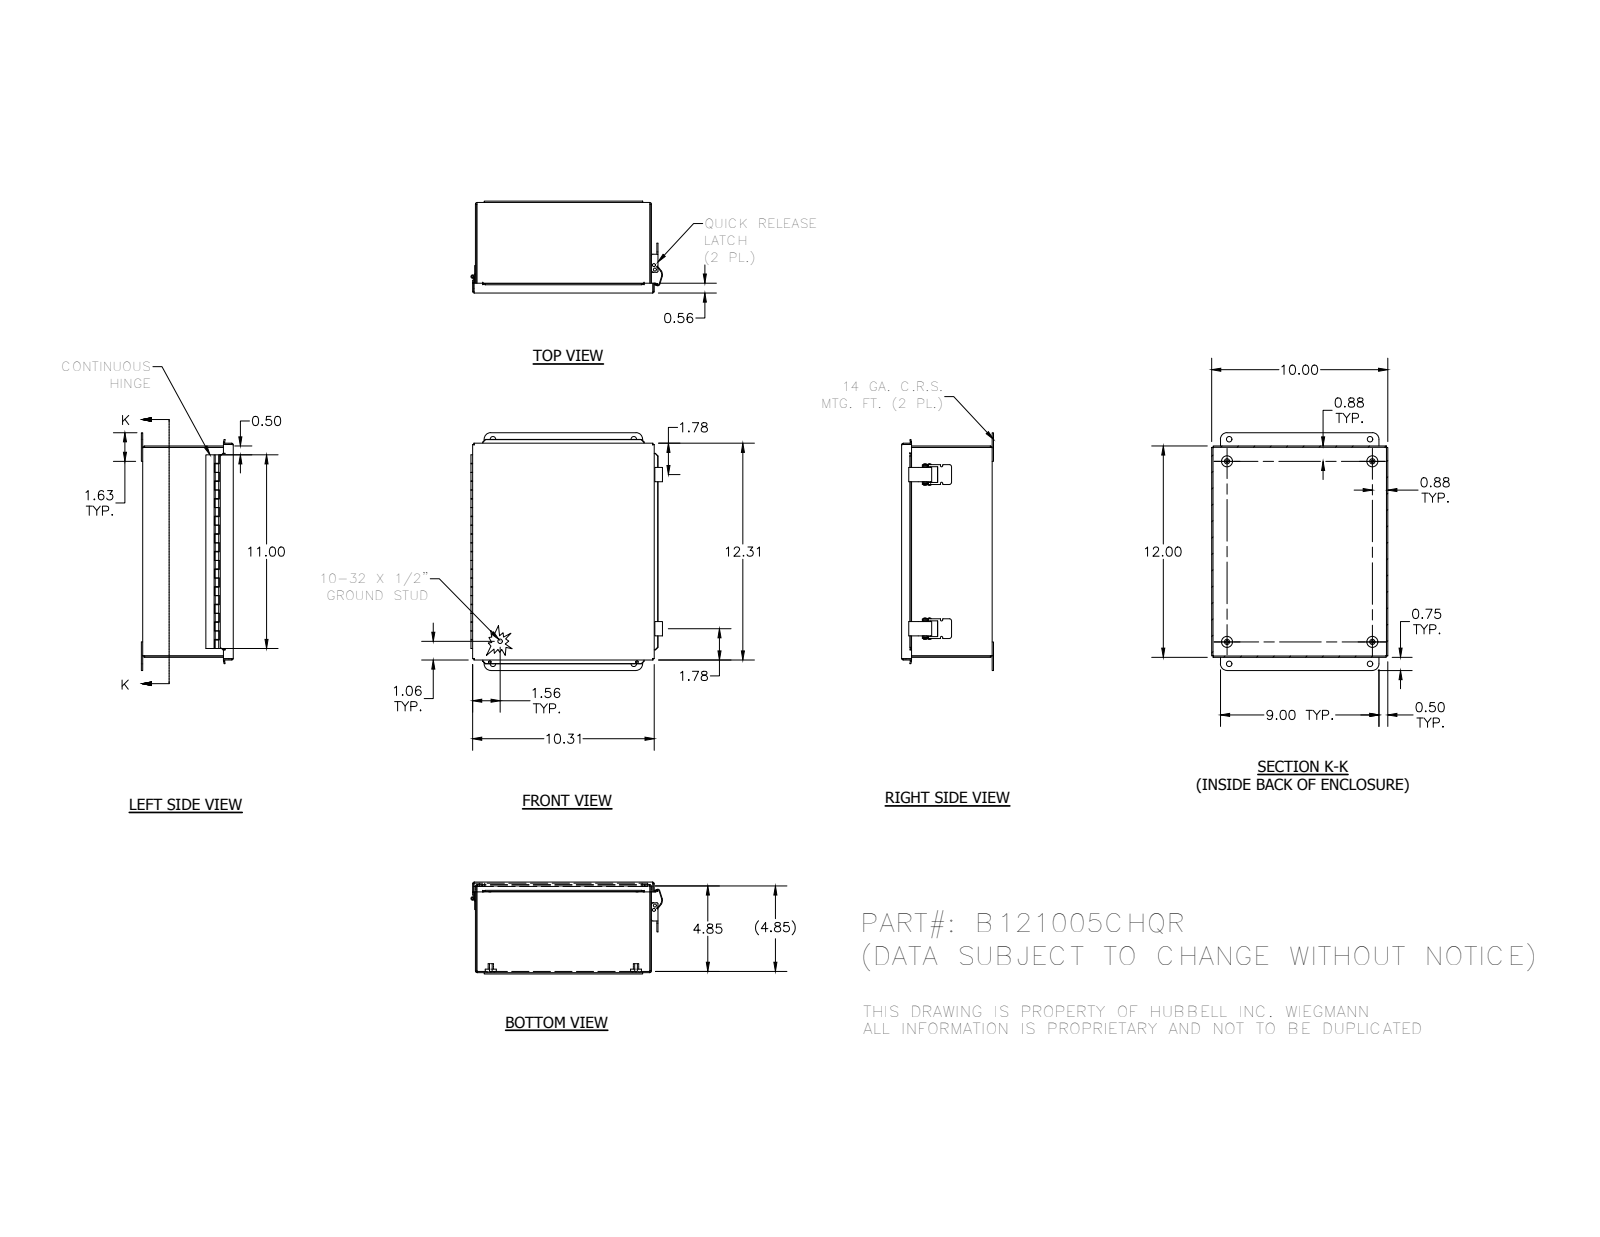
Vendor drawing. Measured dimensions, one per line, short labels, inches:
name: B121005CHQR; 3499; 3484; B121005CHQRBKP (+8 more)
written by: Autodesk Inventor 2012 (AUTOMOTIVE_DESIGN)
unit: in
bodies: 24 solids, 589 faces (363 planar, 179 cylindrical, 47 other)
size: 13.5 × 10.88 × 5.219
volume: 43.84 in³; area: 1 211 in²
holes: 4× ⌀0.156, 4× ⌀0.31, 2× ⌀0.14, 2× ⌀0.155, 1× ⌀0.116, 1× ⌀0.17
bosses: 4× ⌀0.625, 4× ⌀0.3, 2× ⌀0.25, 2× ⌀0.169, 2× ⌀0.136, 1× ⌀0.2, 1× ⌀0.19, 1× ⌀0.1
rounds: 20× R0.031, 8× R0.105, 7× R0.093, 5× R0.063, 4× R0.109, 4× R0.375, 2× R0.125, 1× R0.062
face distances: 0.074, 5.083, 5.144, 0.062, 5.009, 5.07, 9.926, 11.926, 10, 9.852
hole spacings: 1.257, 8.221, 11.501, 14.081, 8, 12.75, 15.052, 0.256
